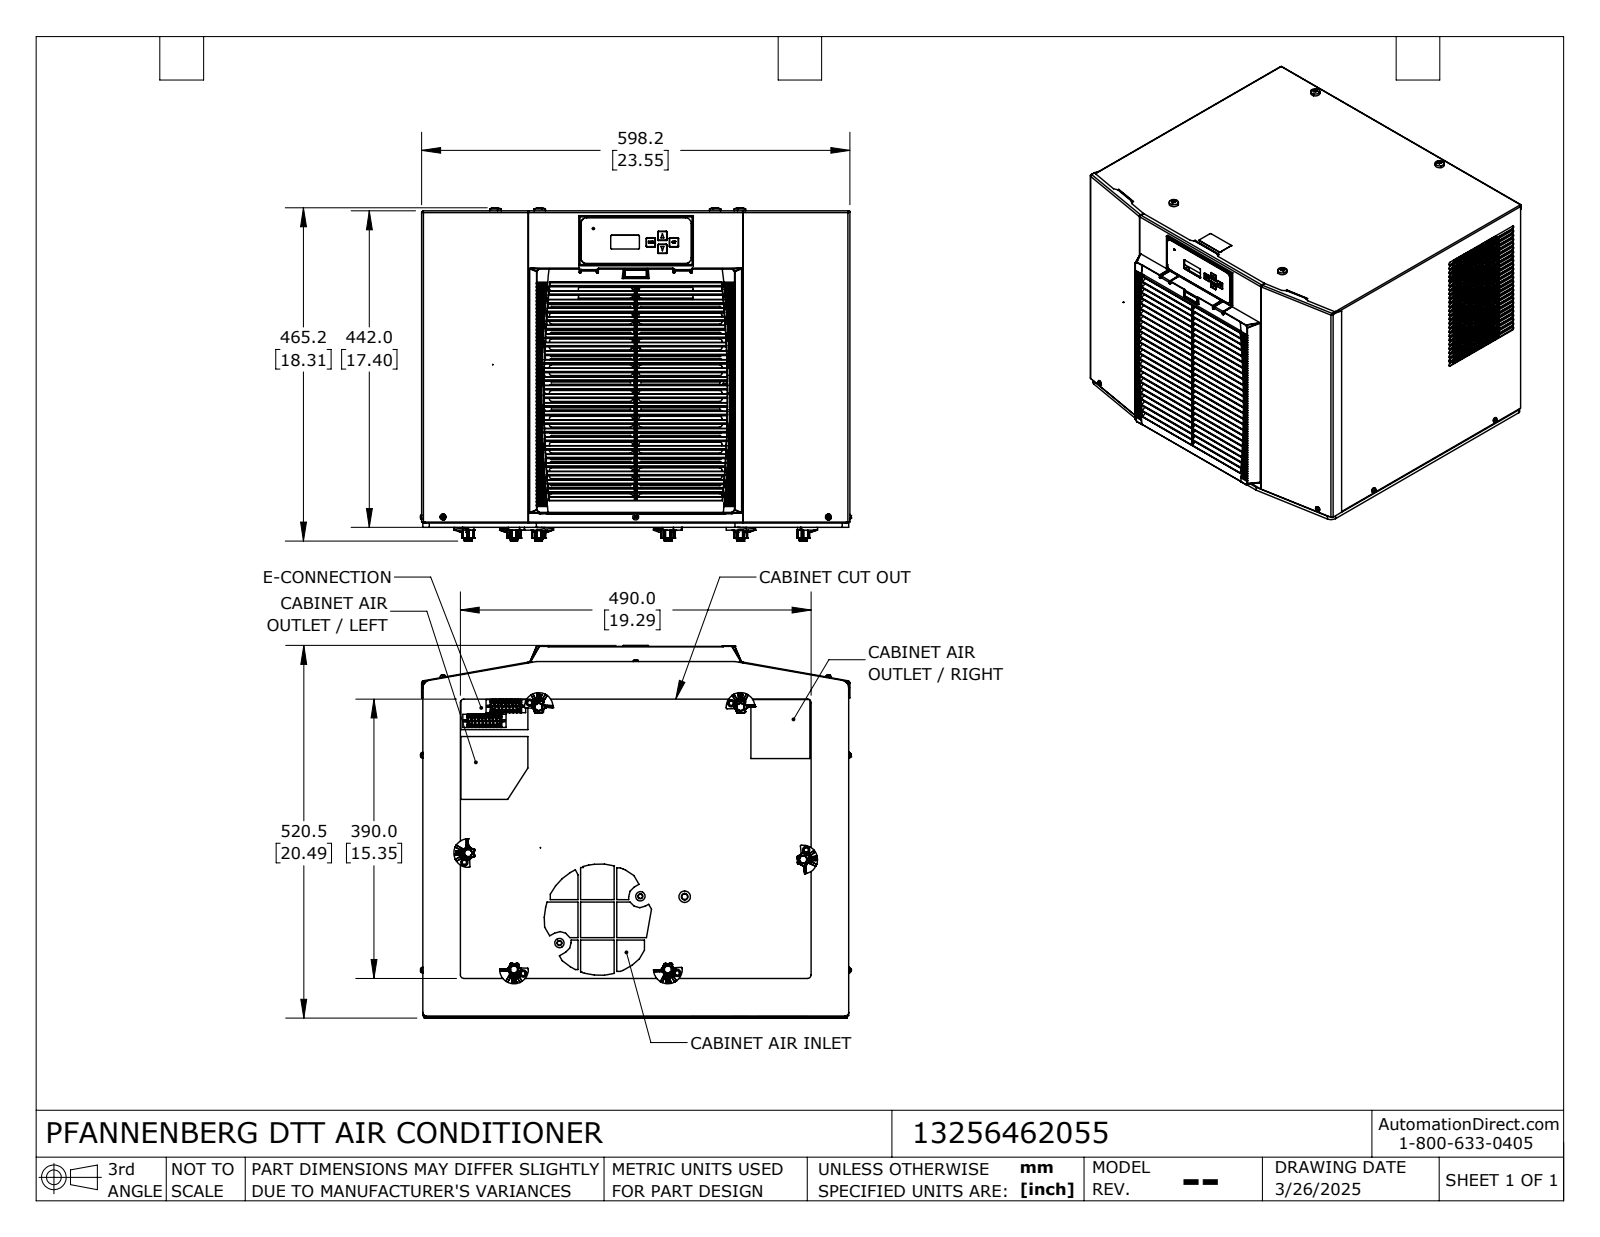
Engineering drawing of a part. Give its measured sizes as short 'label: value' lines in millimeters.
name: 13256462055_Default
written by: SolidWorks 2024 (CONFIG_CONTROL_DESIGN)
unit: mm
bodies: 76 solids, 9236 faces (5187 planar, 2651 cylindrical, 1398 other)
size: 601 × 520.5 × 465.3
volume: 2 769 000 mm³; area: 3 469 000 mm²
holes: 17× ⌀2.3, 13× ⌀6, 12× ⌀6.9, 10× ⌀4.5, 8× ⌀10, 7× ⌀5.5, 6× ⌀3, 6× ⌀5, 6× ⌀6.1, 5× ⌀3.5, 5× ⌀8, 5× ⌀9.2
bosses: 12× ⌀9, 10× ⌀4, 8× ⌀5, 7× ⌀16, 6× ⌀15, 6× ⌀13, 6× ⌀11.8, 5× ⌀11
rounds: 375× R3, 112× R4, 92× R0.5, 78× R0.2, 61× R1, 54× R0.9, 48× R0.1, 42× R0.4
face distances: 1.5, 1, 594, 434.5, 433.5, 432, 433, 595, 593, 493.5
hole spacings: 110, 220, 5, 9, 25, 90, 330, 1.4
